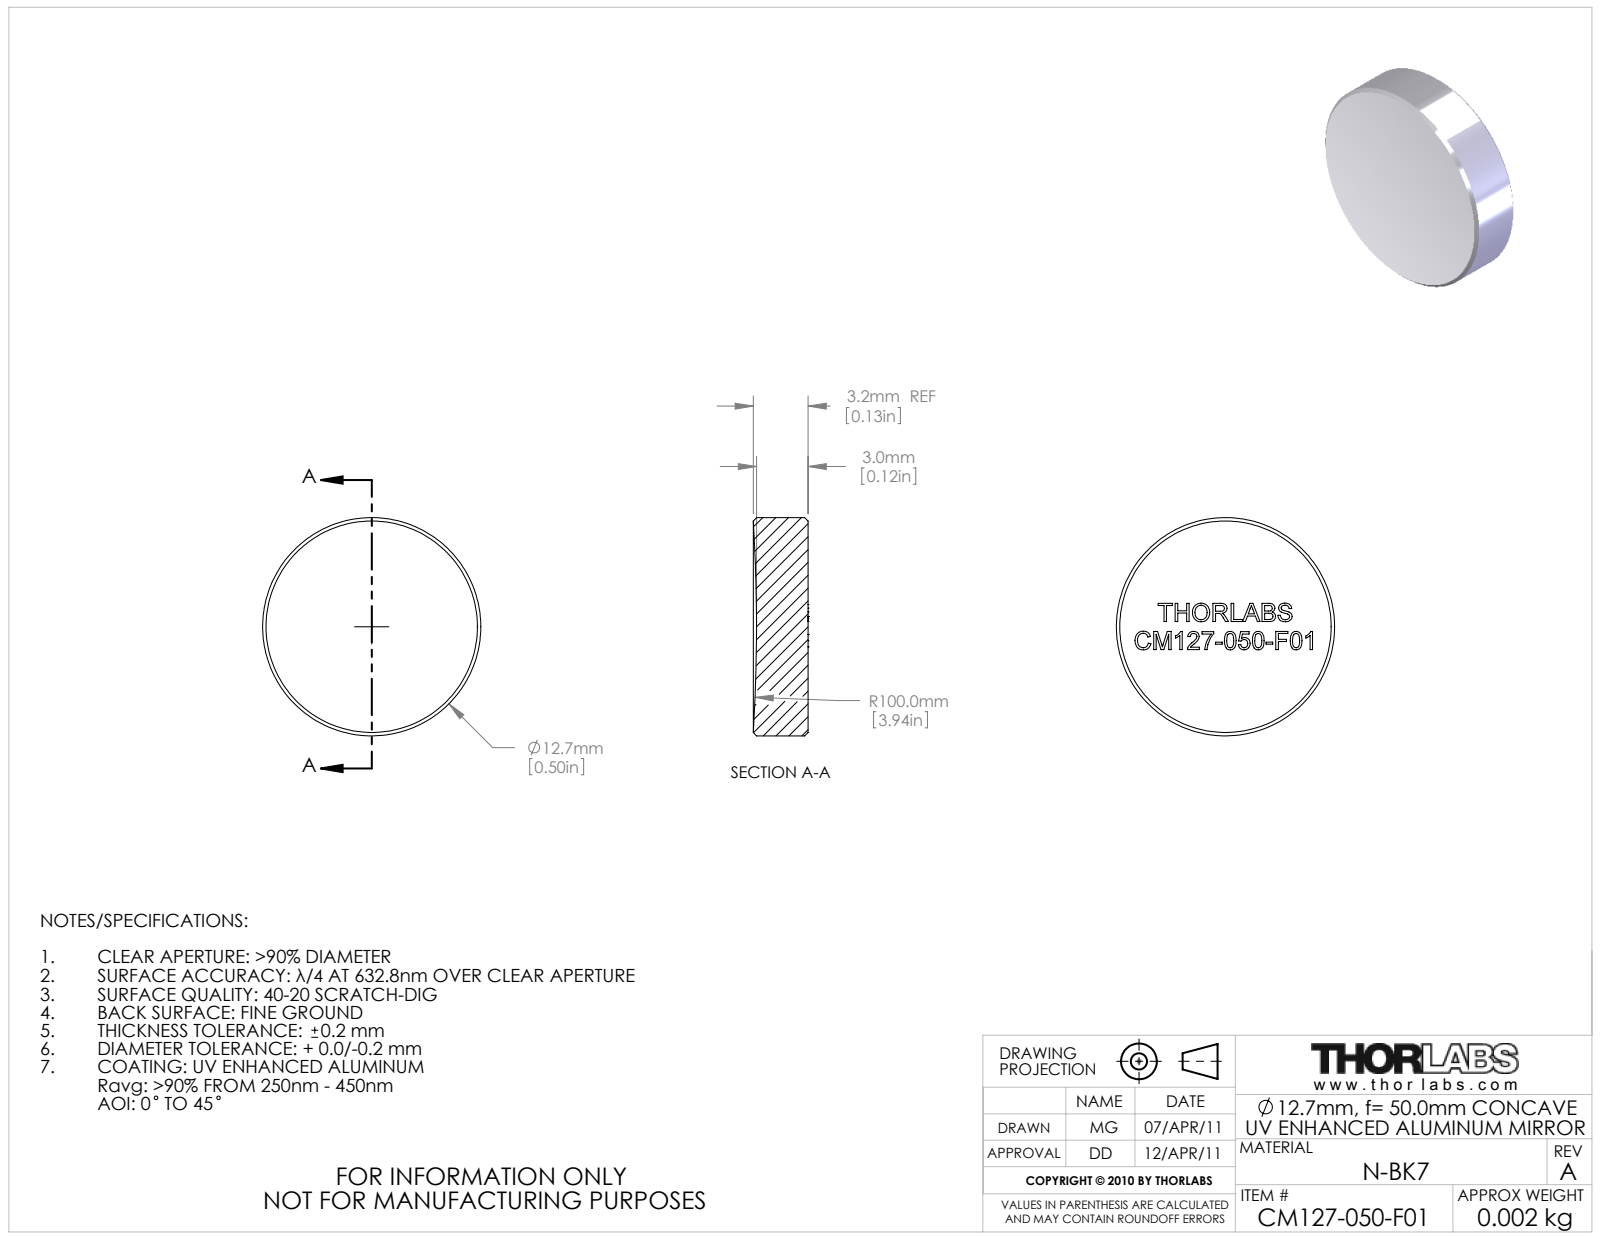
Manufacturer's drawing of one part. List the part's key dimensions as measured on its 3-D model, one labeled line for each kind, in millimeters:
Part name (STEP PRODUCT): 22193-E0W
STEP written by: SolidWorks 2011 (AUTOMOTIVE_DESIGN)
Units: millimetres
Bodies: 1 solid, 263 faces (148 planar, 2 cylindrical, 113 other)
Overall size (bounding box): 12.7 × 12.7 × 3.2
Volume: 390 mm³ · Surface area: 372 mm²
Round bosses / shafts (diameter × count): ⌀12.7 ×1
Main face-to-face distances: 1.1, 1.3, 1.6, 0.9, 1, 0.6, 1.7, 2.8, 1.5, 0.7
